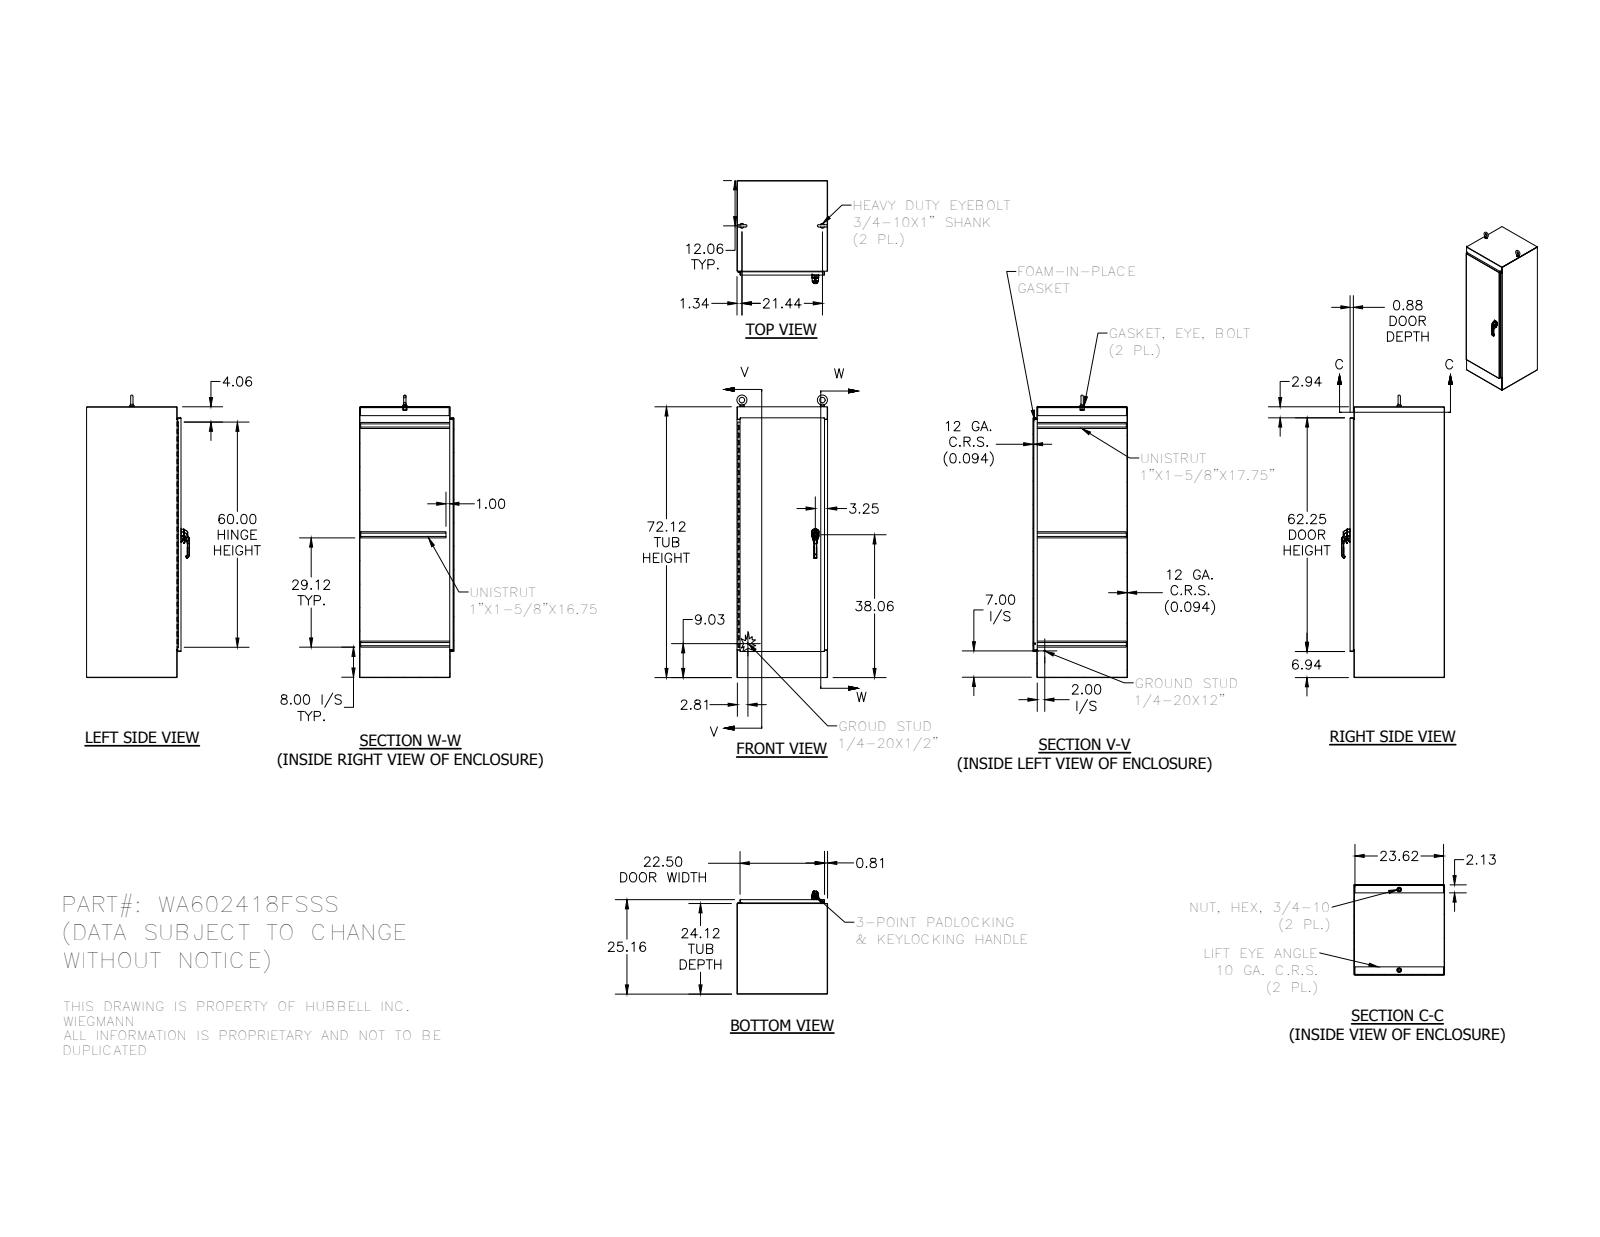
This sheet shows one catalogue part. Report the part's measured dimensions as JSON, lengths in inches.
{"part_name": "WA722424FSBLS; WA7224FSRS; WA2424FSTOP; WA2424FSBTM (+8 more)", "step_written_by": "Autodesk Inventor 2014 (AUTOMOTIVE_DESIGN)", "units": "inches", "bodies": {"solids": 46, "faces": 2855, "planar": 1212, "cylindrical": 995, "other": 648}, "overall_size": [75.248, 27.409, 24.125], "volume_in3": 895.2, "surface_area_in2": 18940, "round_holes": [[0.276, 8], [0.2, 4], [0.213, 3], [0.28, 3], [0.315, 2], [0.402, 2], [0.407, 2], [0.413, 2], [0.642, 2], [0.813, 2], [0.122, 1], [0.124, 1]], "round_bosses_or_shafts": [[0.25, 3], [1.25, 2], [1.12, 2], [0.75, 2], [0.531, 2], [0.526, 2], [0.435, 2], [0.337, 2]], "partial_cylinders_radius": [[0.02, 178], [0.012, 101], [0.019, 23], [0.01, 16], [0.031, 15], [0.079, 14], [0.125, 13], [0.019, 12]], "face_to_face_distances": [0.094, 24.031, 25.067, 23.938, 24.125, 24.973, 25.161, 72.031, 1.035, 71.938], "hole_center_spacings": [0.38, 0.382, 0.382, 0.762, 0.764, 0.886, 1.144, 1.271]}
